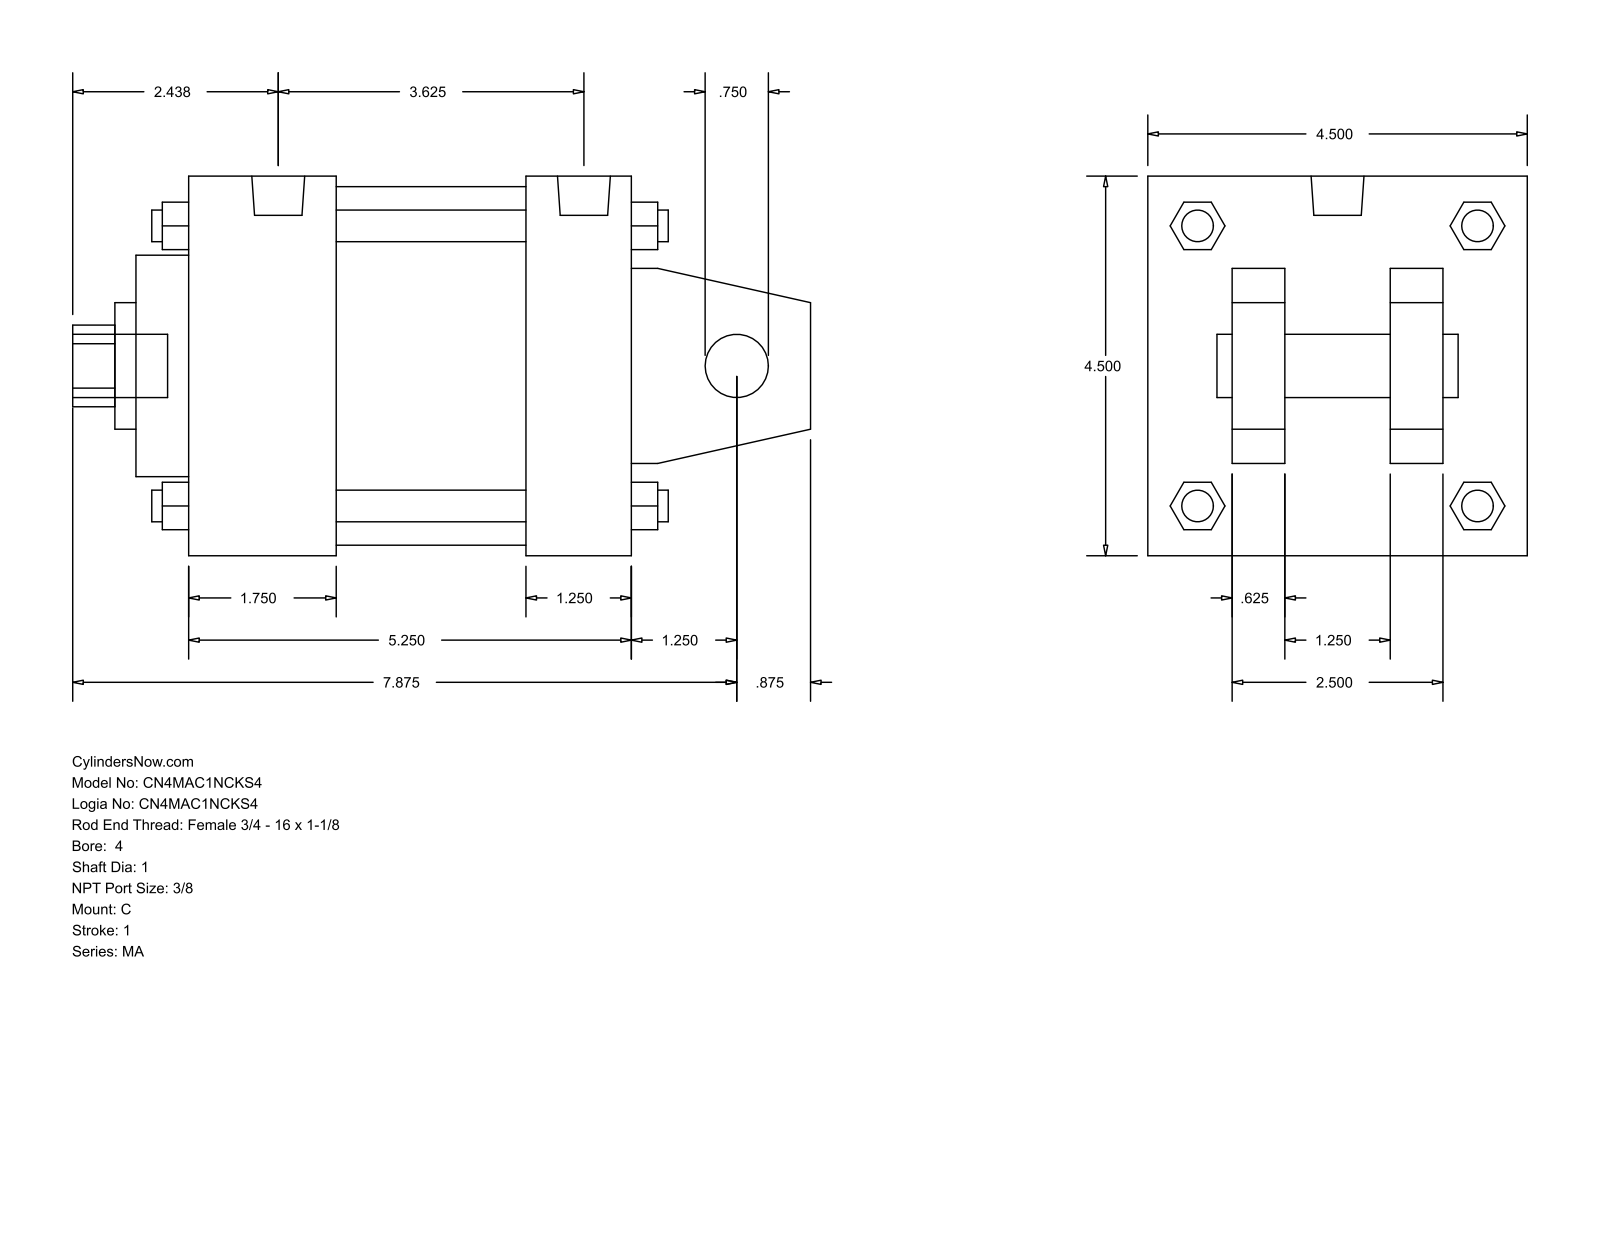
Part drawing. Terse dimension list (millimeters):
name: MA_C__0400_1
written by: GSSL Pune (CONFIG_CONTROL_DESIGN)
unit: mm
bodies: 0 solids, 141 faces (109 planar, 32 cylindrical, 0 other)
size: 222.25 × 114.3 × 114.3
holes: 1× ⌀19.05, 1× ⌀25.4, 1× ⌀38.1, 1× ⌀66.67, 1× ⌀107.95
bosses: 4× ⌀11.11, 4× ⌀9.53, 2× ⌀15.93, 1× ⌀19.05
rounds: 1× R12.29
face distances: 114.3, 133.36, 88.9, 15.87, 73.03, 41.27, 25.4, 47.63, 101.61, 31.75
